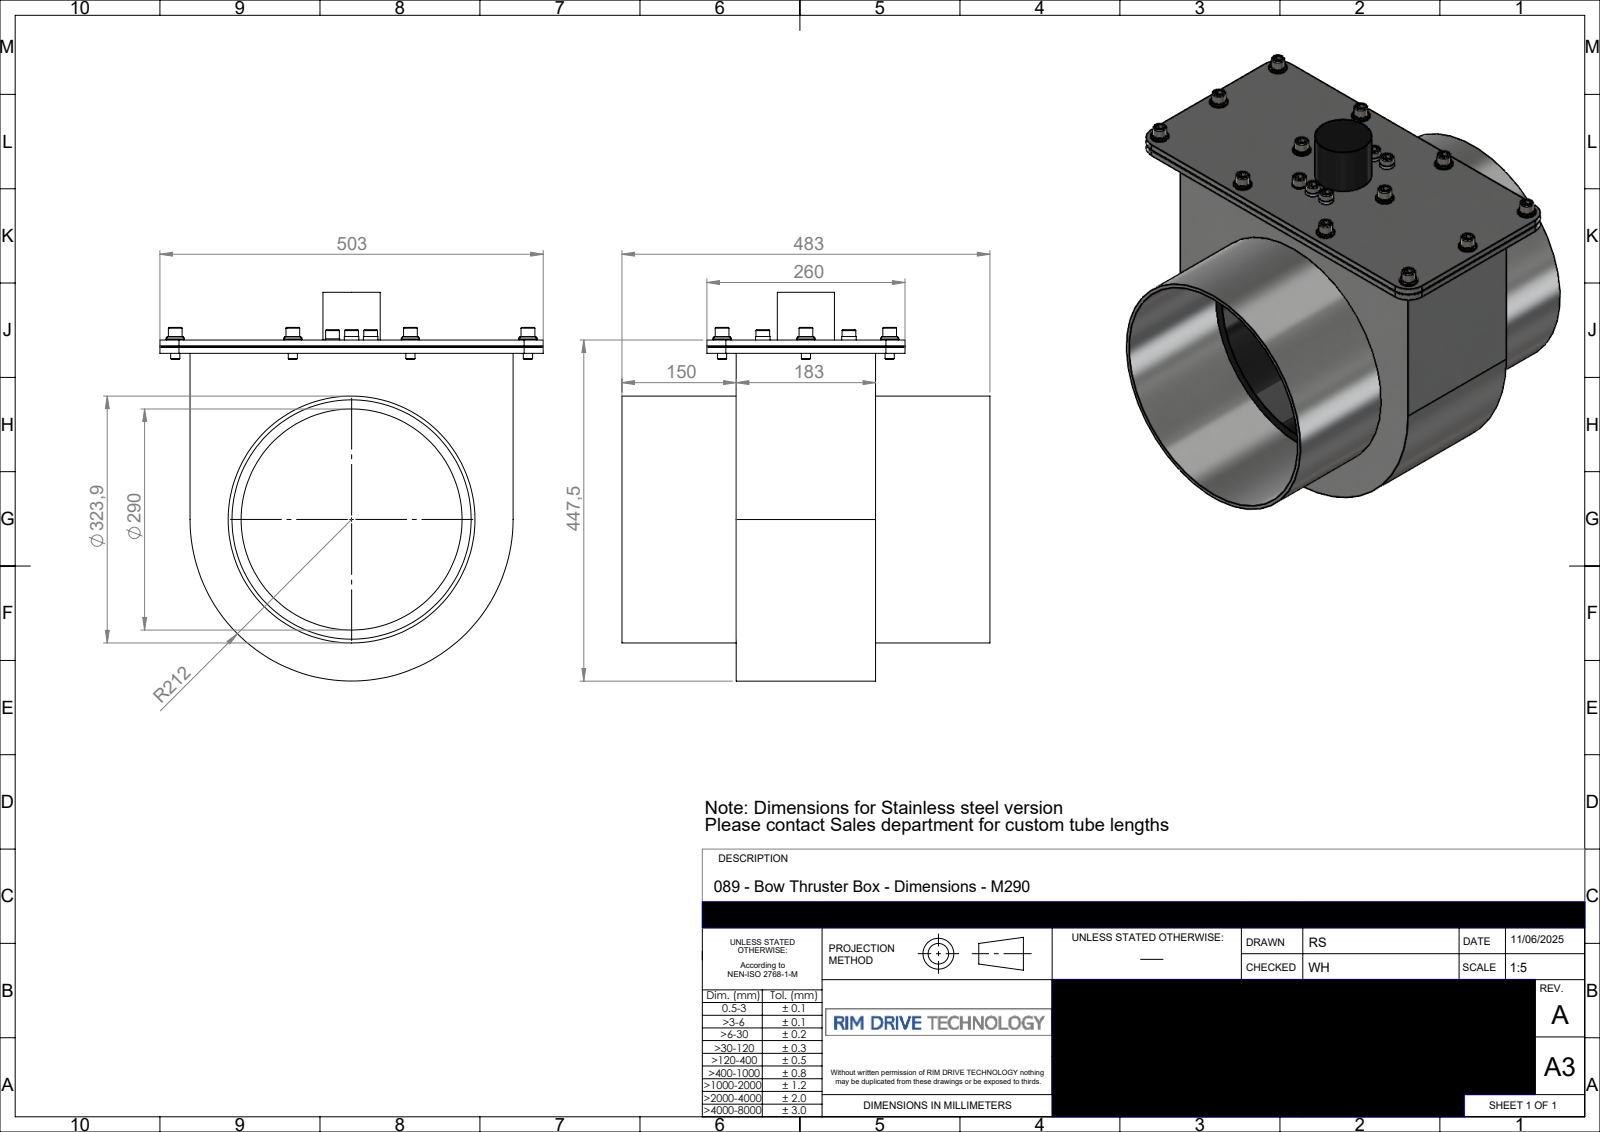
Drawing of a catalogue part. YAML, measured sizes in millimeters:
part_name: "P-089-030-rev-A-M290"
step_written_by: "SolidWorks 2024 (AUTOMOTIVE_DESIGN)"
units: millimeters
bodies: {solids: 1, faces: 458, planar: 301, cylindrical: 89, other: 68}
overall_size: [510, 503, 483]
volume: 21630000
surface_area: 1413000
round_holes:
  - {diameter: 12.7, count: 2}
  - {diameter: 290, count: 1}
  - {diameter: 313.9, count: 1}
round_bosses_or_shafts:
  - {diameter: 18, count: 18}
  - {diameter: 24, count: 12}
  - {diameter: 21.1, count: 12}
  - {diameter: 12, count: 12}
  - {diameter: 19, count: 6}
  - {diameter: 323.9, count: 1}
  - {diameter: 75, count: 1}
partial_cylinders:
  - {radius: 0.1, count: 8}
  - {radius: 25, count: 4}
  - {radius: 212, count: 1}
face_to_face_distances: [183, 17.5, 424, 38.5, 221.5, 11, 10.95, 172, 161.05, 172.05]
hole_center_spacings: [113]
